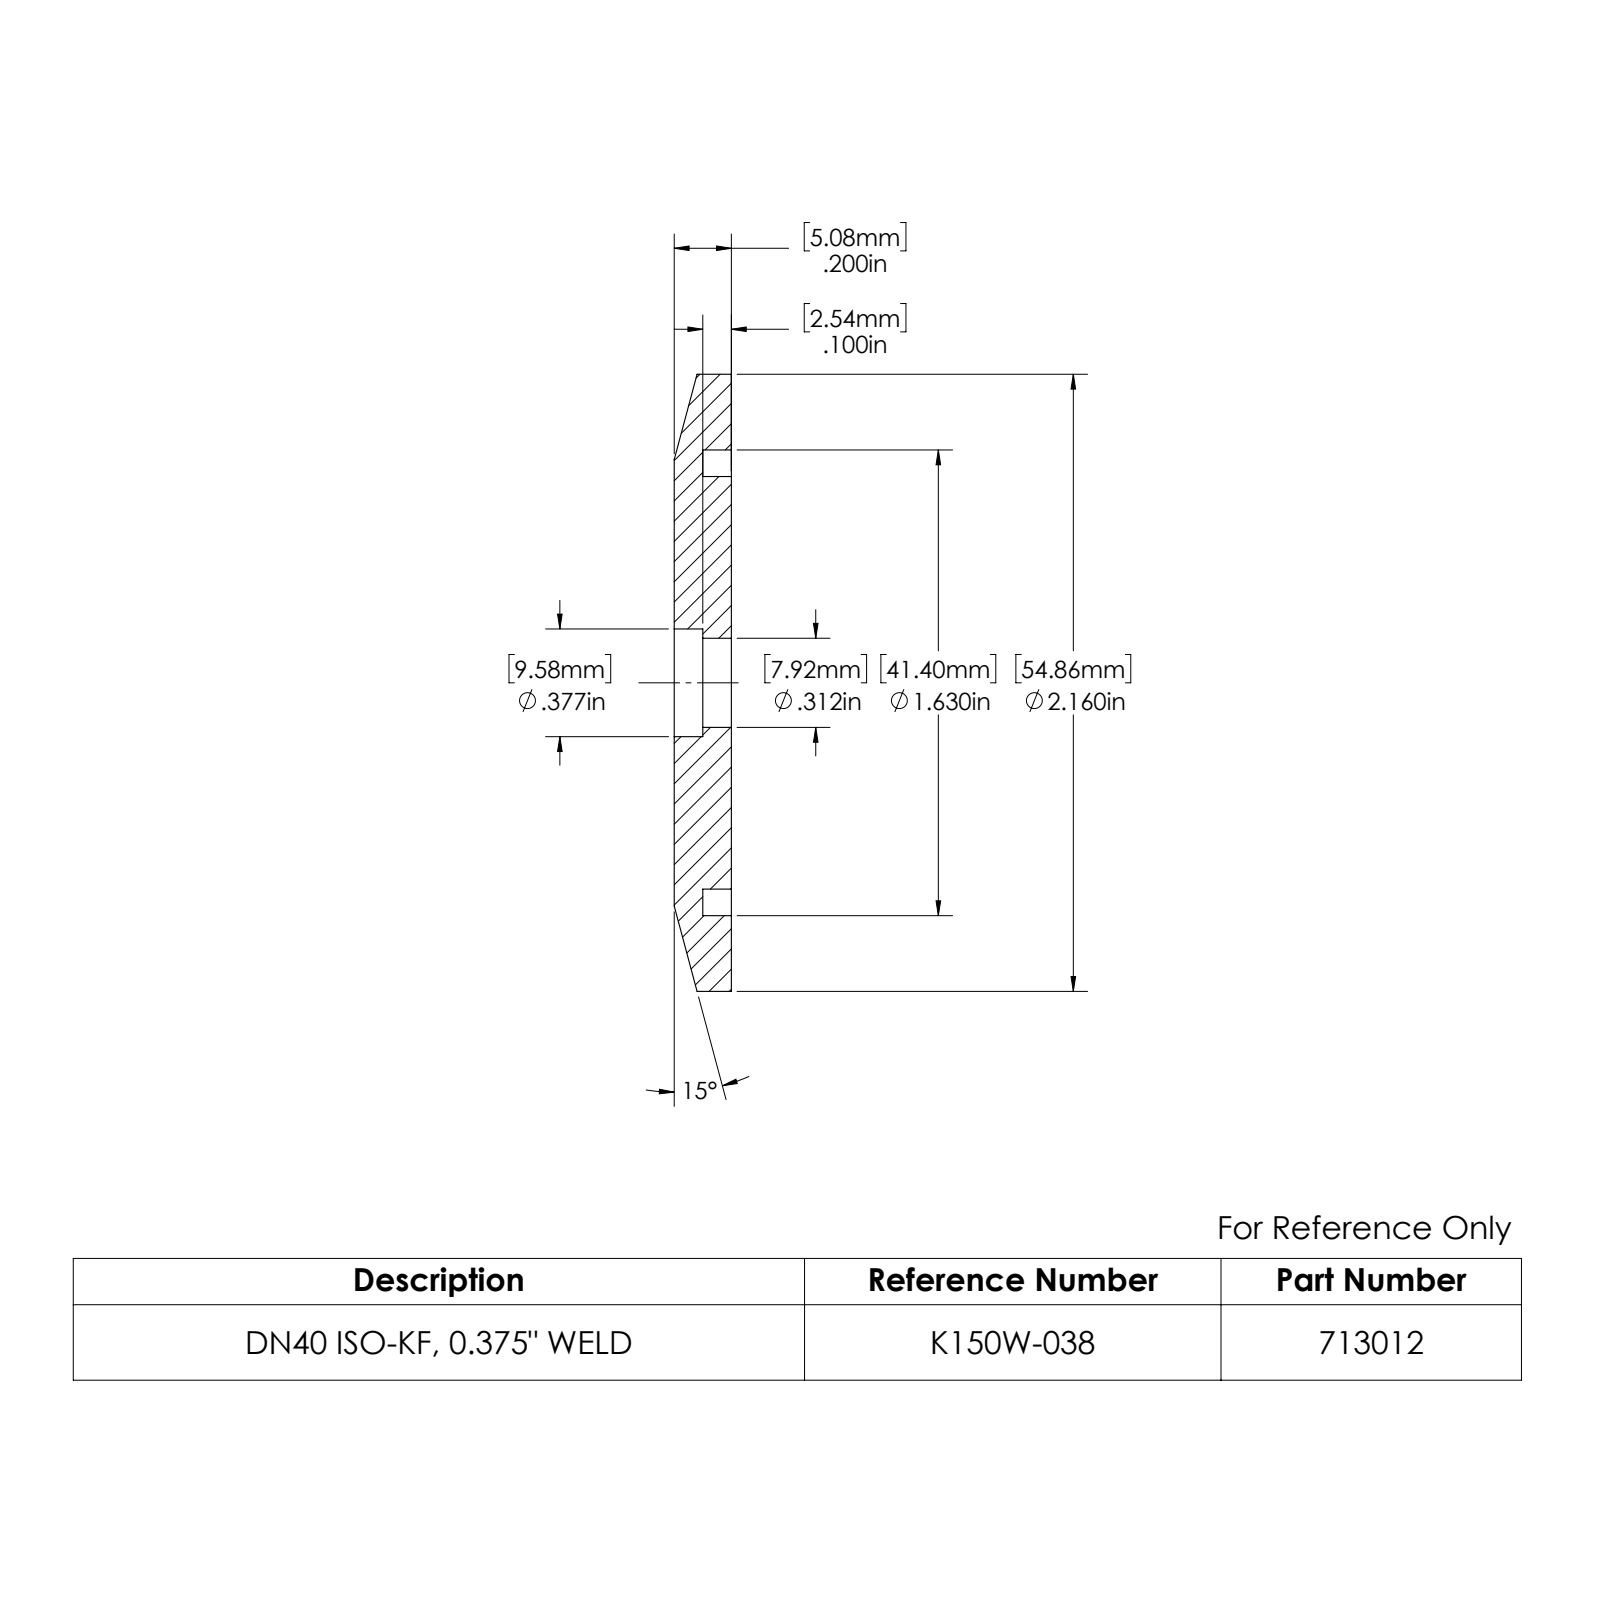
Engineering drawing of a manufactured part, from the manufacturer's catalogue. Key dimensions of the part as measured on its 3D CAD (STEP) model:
Part name (STEP PRODUCT): 713012
STEP written by: SolidWorks 2022 (AUTOMOTIVE_DESIGN)
Units: inches
Bodies: 1 solid, 17 faces (5 planar, 10 cylindrical, 2 other)
Overall size (bounding box): 2.16 × 2.16 × 0.2
Volume: 0.596 in³ · Surface area: 9.234 in²
Round holes (diameter × count): ⌀0.312 ×1, ⌀0.377 ×1, ⌀1.63 ×1
Round bosses / shafts (diameter × count): ⌀2.16 ×1, ⌀1.444 ×1
Main face-to-face distances: 0.2, 0.1
